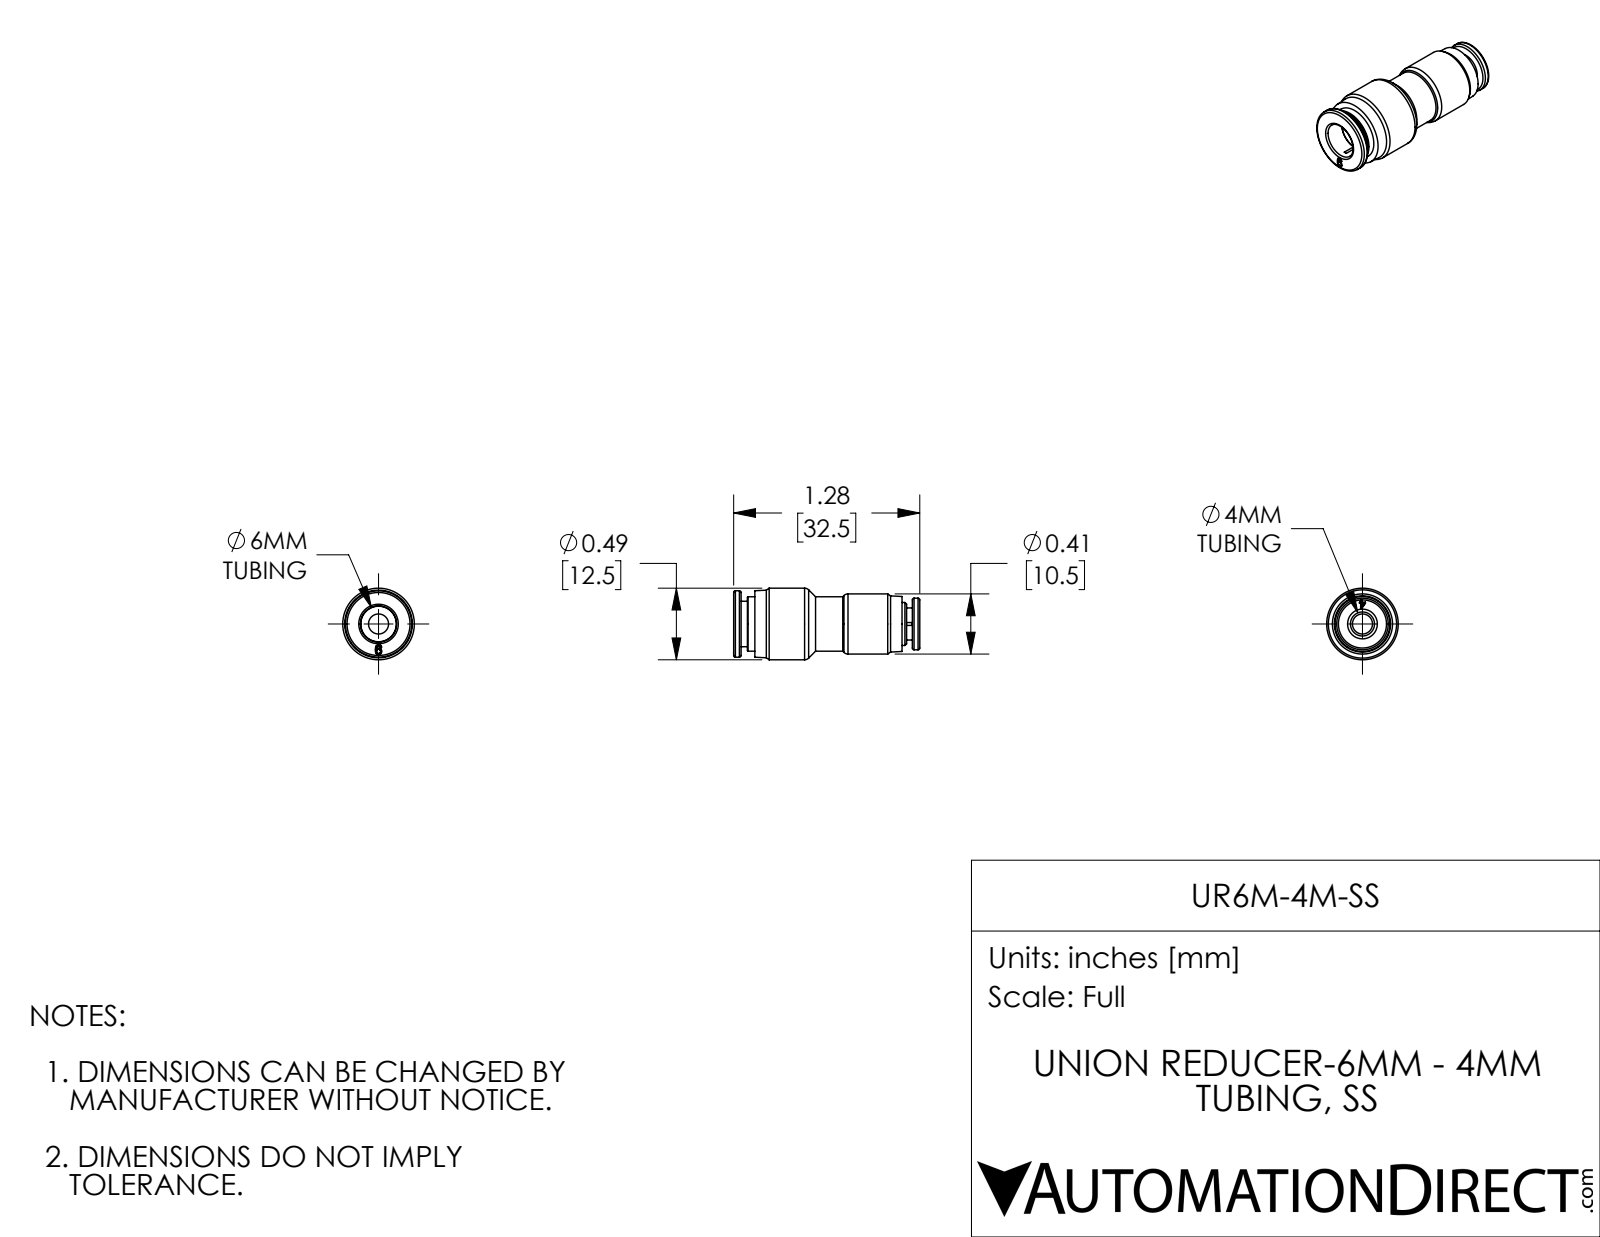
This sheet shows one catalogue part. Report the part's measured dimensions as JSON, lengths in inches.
{"part_name": "UR6M-4M-SS", "step_written_by": "SolidWorks 2017 (AUTOMOTIVE_DESIGN)", "units": "inches", "bodies": {"solids": 1, "faces": 123, "planar": 43, "cylindrical": 28, "other": 52}, "overall_size": [1.28, 0.492, 0.492], "volume_in3": 0.13, "surface_area_in2": 3.164, "round_holes": [[0.138, 1], [0.165, 1], [0.244, 1], [0.248, 1], [0.319, 1]], "round_bosses_or_shafts": [[0.492, 1], [0.457, 1], [0.413, 1], [0.374, 1], [0.354, 1], [0.313, 1], [0.295, 1], [0.22, 1]], "face_to_face_distances": [0.051, 1.228, 0.094, 1.134, 0.146, 1.28, 1.177, 1.083, 0.122, 0.071]}
